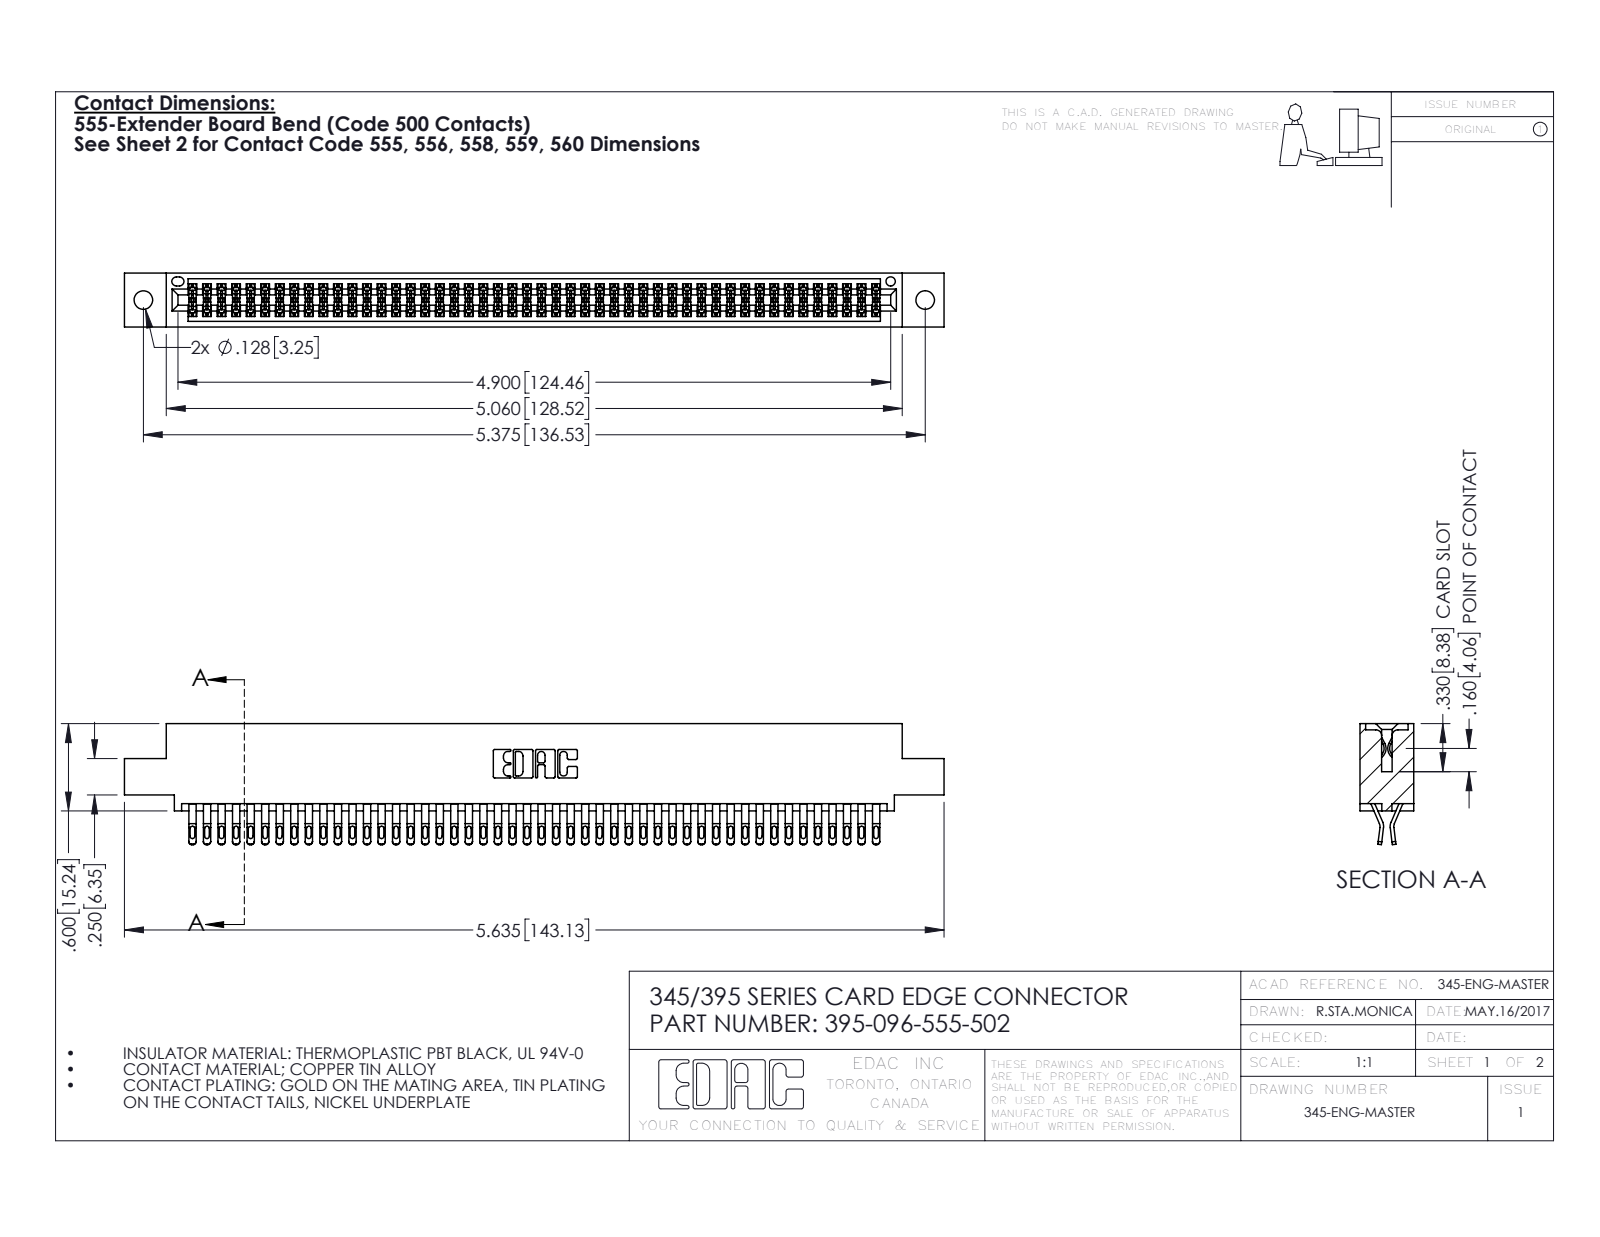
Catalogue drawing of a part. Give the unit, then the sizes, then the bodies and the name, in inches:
Units: inches
Overall size (bounding box): 5.635 × 0.832 × 0.37
Round holes (diameter × count): ⌀0.128 ×2, ⌀0.064 ×1
Partial cylindrical surfaces — rounded edges, fillets, slot ends (radius × count): R0.016 ×240, R0.02 ×192, R0.006 ×144, R0.01 ×22, R0.007 ×6, R0.031 ×6, R0.026 ×3, R0.01 ×2
Main face-to-face distances: 0.298, 0.072, 0.025, 0.37, 0.2, 0.098, 0.272, 0.225, 0.175, 0.149
Hole centre spacings: 0.27, 5.139, 5.375
Volume: 0.862 in³ · Surface area: 33.77 in²
Bodies: 97 solids, 5506 faces (3060 planar, 2446 cylindrical, 0 other)
Part name (STEP PRODUCT): 395-096-555-502; 345-292-001_555 Tail; 345 Part_0.110 Offset - 0.128 Dia
STEP written by: SolidWorks 2016 (CONFIG_CONTROL_DESIGN)
